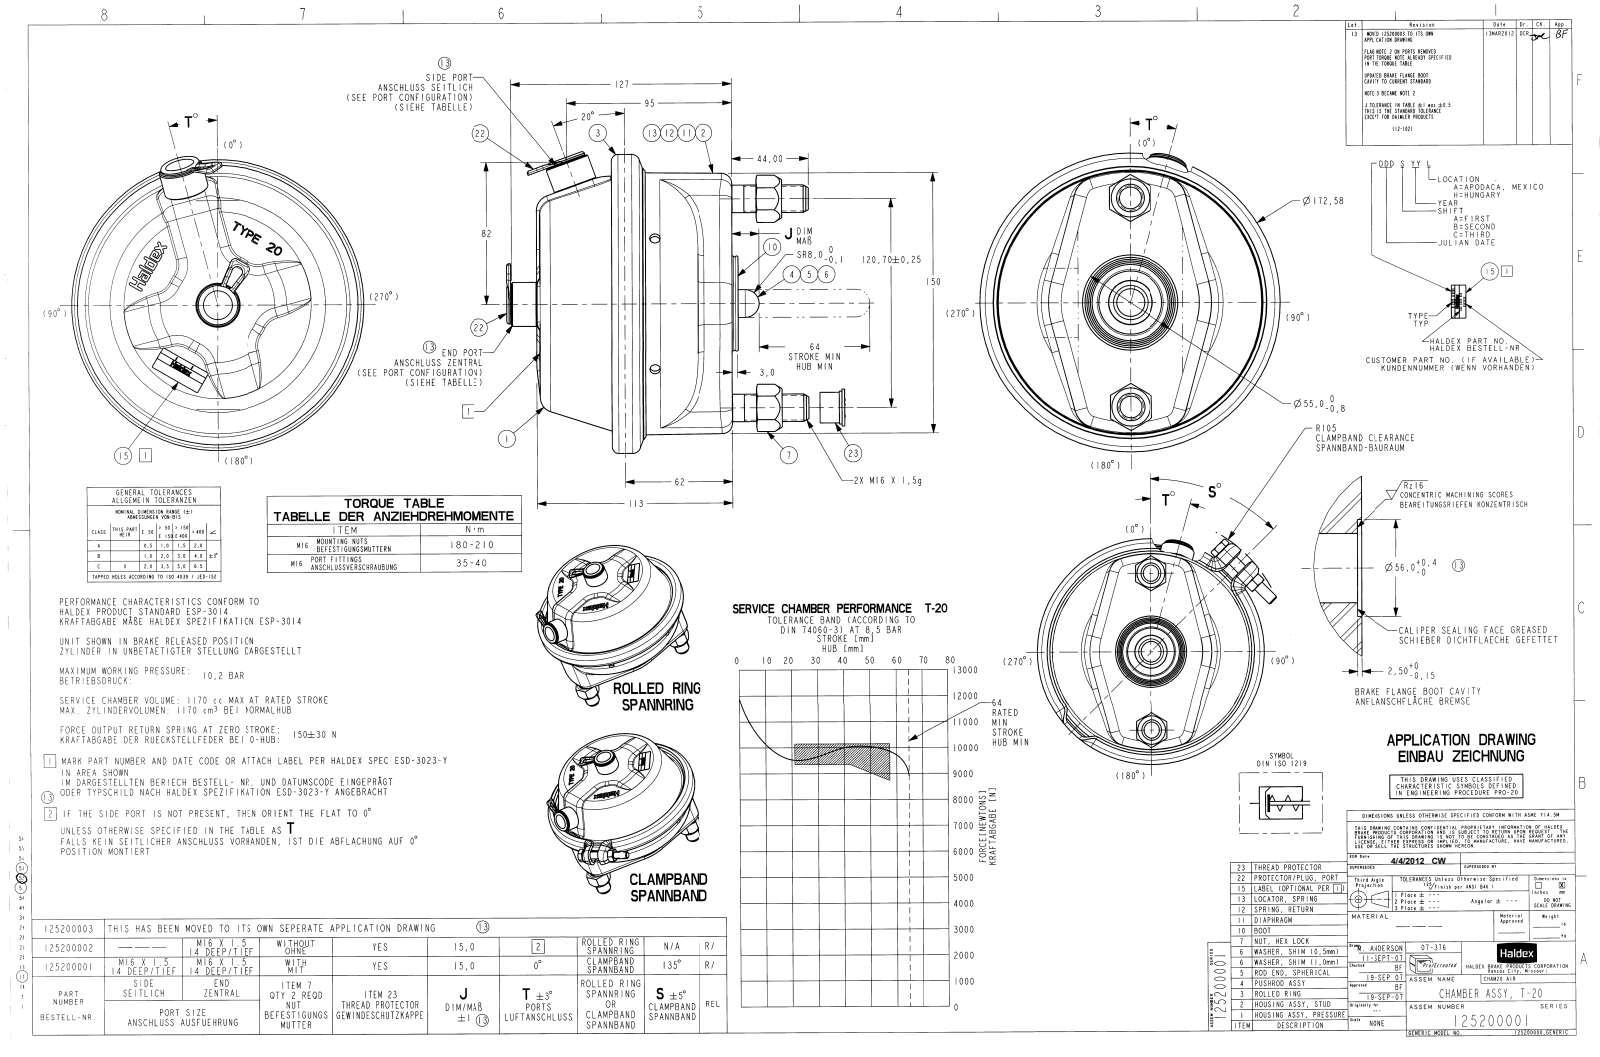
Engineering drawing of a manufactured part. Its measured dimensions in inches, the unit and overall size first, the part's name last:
Units: inches
Overall size (bounding box): 7.313 × 6.993 × 6.884
Round holes (diameter × count): ⌀0.236 ×3, ⌀0.354 ×2, ⌀0.571 ×2, ⌀0.695 ×2, ⌀0.776 ×2, ⌀0.24 ×1, ⌀0.394 ×1, ⌀0.402 ×1, ⌀0.409 ×1, ⌀0.531 ×1, ⌀0.63 ×1, ⌀1.437 ×1
Round bosses / shafts (diameter × count): ⌀0.63 ×3, ⌀0.894 ×2, ⌀0.866 ×2, ⌀0.774 ×2, ⌀0.72 ×2, ⌀0.681 ×2, ⌀0.635 ×2, ⌀0.624 ×2
Partial cylindrical surfaces — rounded edges, fillets, slot ends (radius × count): R0.01 ×26, R0.022 ×18, R0.025 ×18, R0.004 ×17, R0.05 ×14, R0.157 ×14, R0.011 ×11, R0.012 ×11
Main face-to-face distances: 0.118, 4.18, 3.959, 0.126, 4.054, 0.197, 4.172, 4.298, 0.079, 0.016
Hole centre spacings: 2.376, 0.906, 1.47, 3.846, 4.752
Volume: 34.62 in³ · Surface area: 616.9 in²
Bodies: 25 solids, 2827 faces (1204 planar, 559 cylindrical, 1064 other)
Part name (STEP PRODUCT): 2056027; 9999272_AF0; 9999272_AF1; 2056019_ASM (+8 more)
STEP written by: CREO PARAMETRIC BY PTC INC, 2018500 (AUTOMOTIVE_DESIGN)
